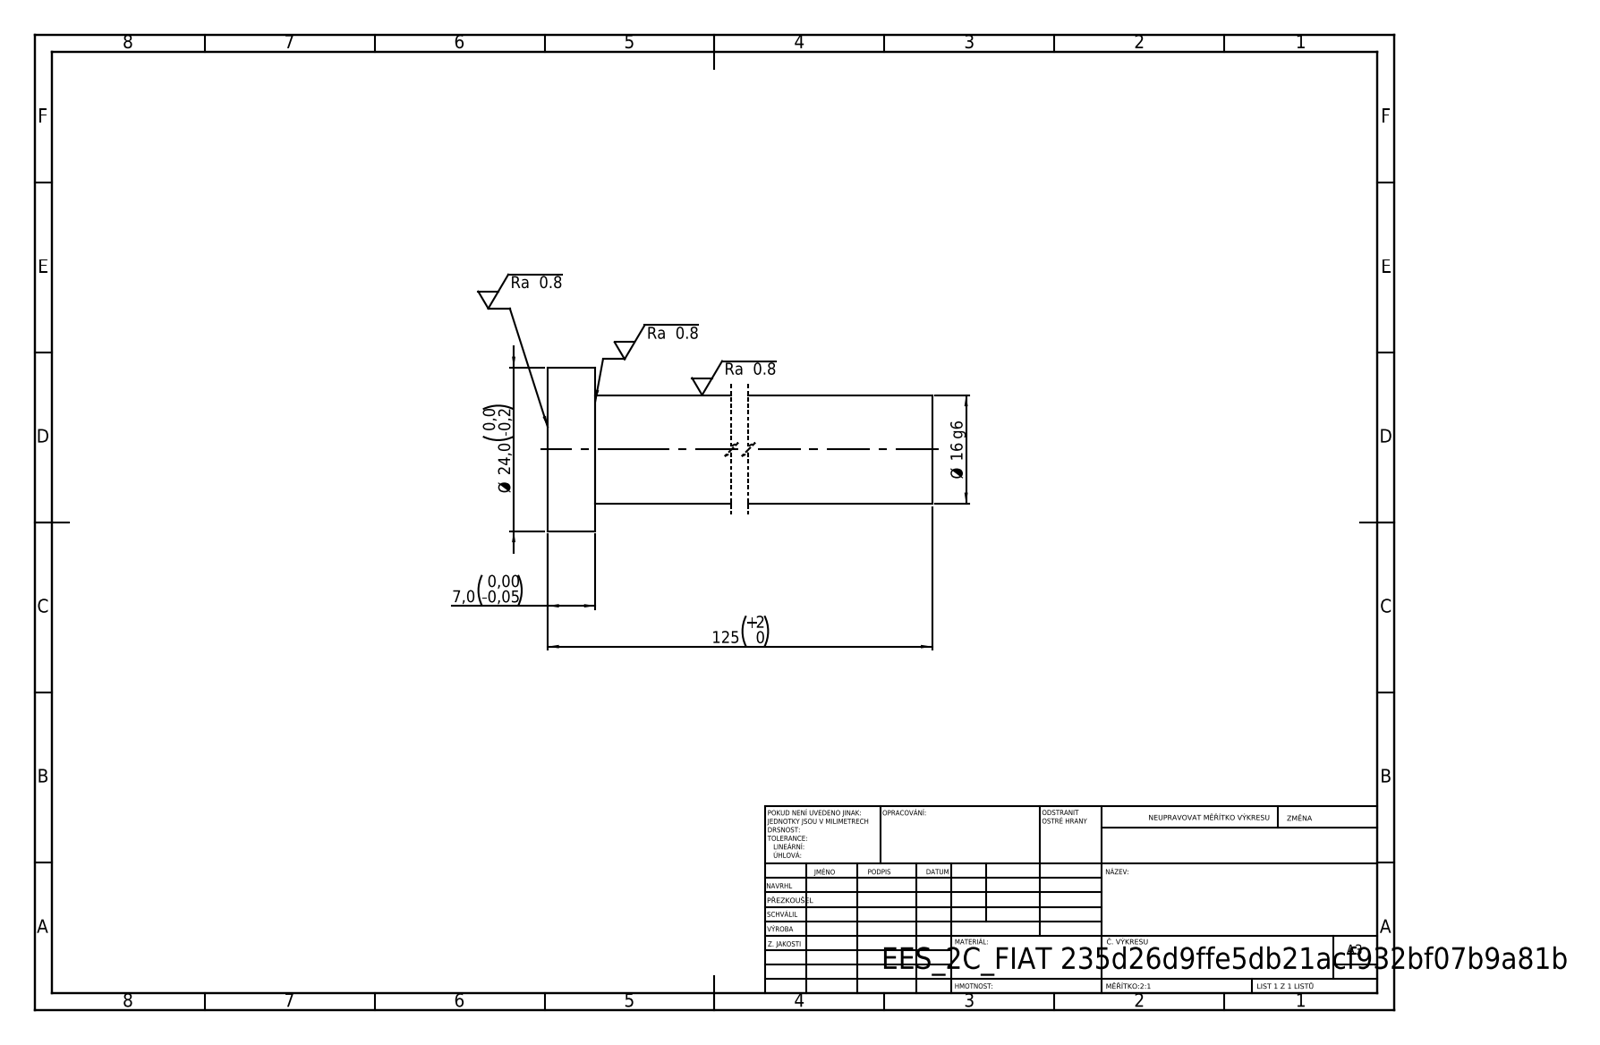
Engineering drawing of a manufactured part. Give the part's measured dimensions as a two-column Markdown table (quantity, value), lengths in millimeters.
| quantity | value |
| --- | --- |
| STEP written by | SolidWorks 2019 (CONFIG_CONTROL_DESIGN) |
| units | millimeters |
| bodies | 1 solid, 7 faces (3 planar, 4 cylindrical, 0 other) |
| overall size | 125 × 24 × 24 |
| volume | 26 892 mm³ |
| surface area | 7 364 mm² |
| round bosses / shafts (diameter × count) | 24 × 1, 16 × 1 |
| main face-to-face distances | 7, 125, 118 |
